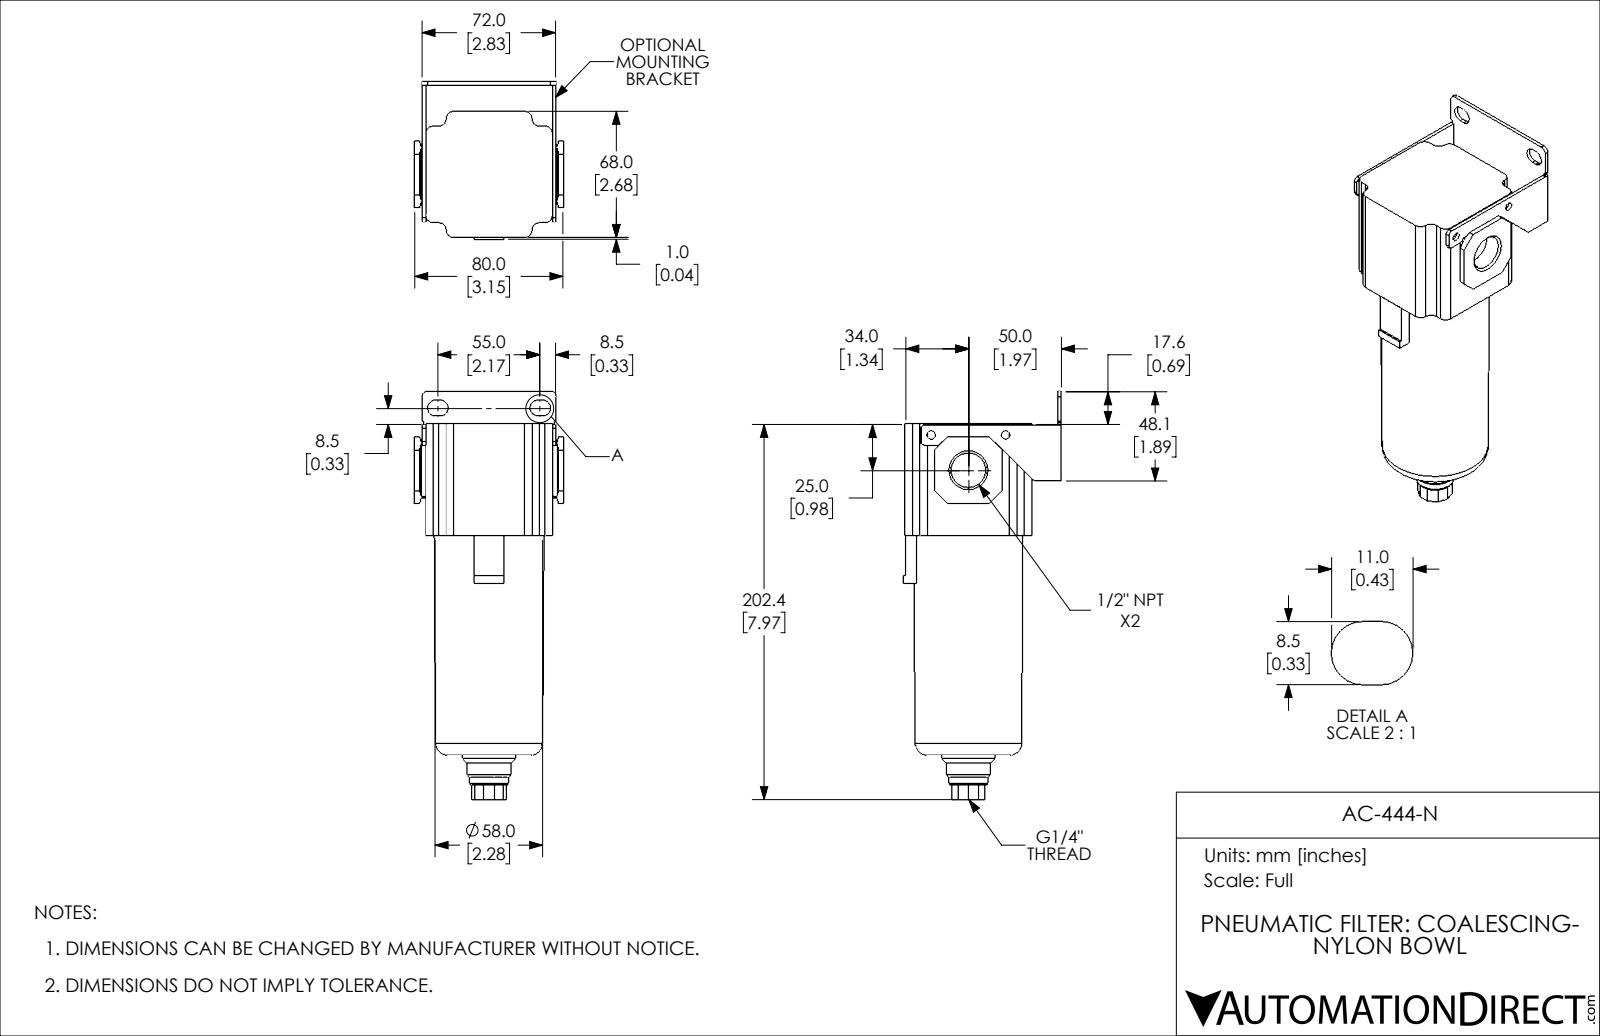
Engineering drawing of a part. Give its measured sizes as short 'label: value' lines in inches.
name: AC-444-N
written by: SolidWorks 2018 (AUTOMOTIVE_DESIGN)
unit: in
bodies: 1 solid, 166 faces (102 planar, 48 cylindrical, 16 other)
size: 8.661 × 3.346 × 3.15
volume: 35.81 in³; area: 94.13 in²
holes: 2× ⌀0.177, 1× ⌀0.451, 1× ⌀0.734
bosses: 1× ⌀1.102, 1× ⌀0.906, 1× ⌀0.787
rounds: 12× R0.157, 4× R0.167, 3× R0.079, 2× R0.039, 2× R0.118
face distances: 0.079, 2.677, 2.756, 0.63, 2.362, 3.307, 0.551, 3.228, 0.157, 0.236
hole spacings: 1.086, 1.575
